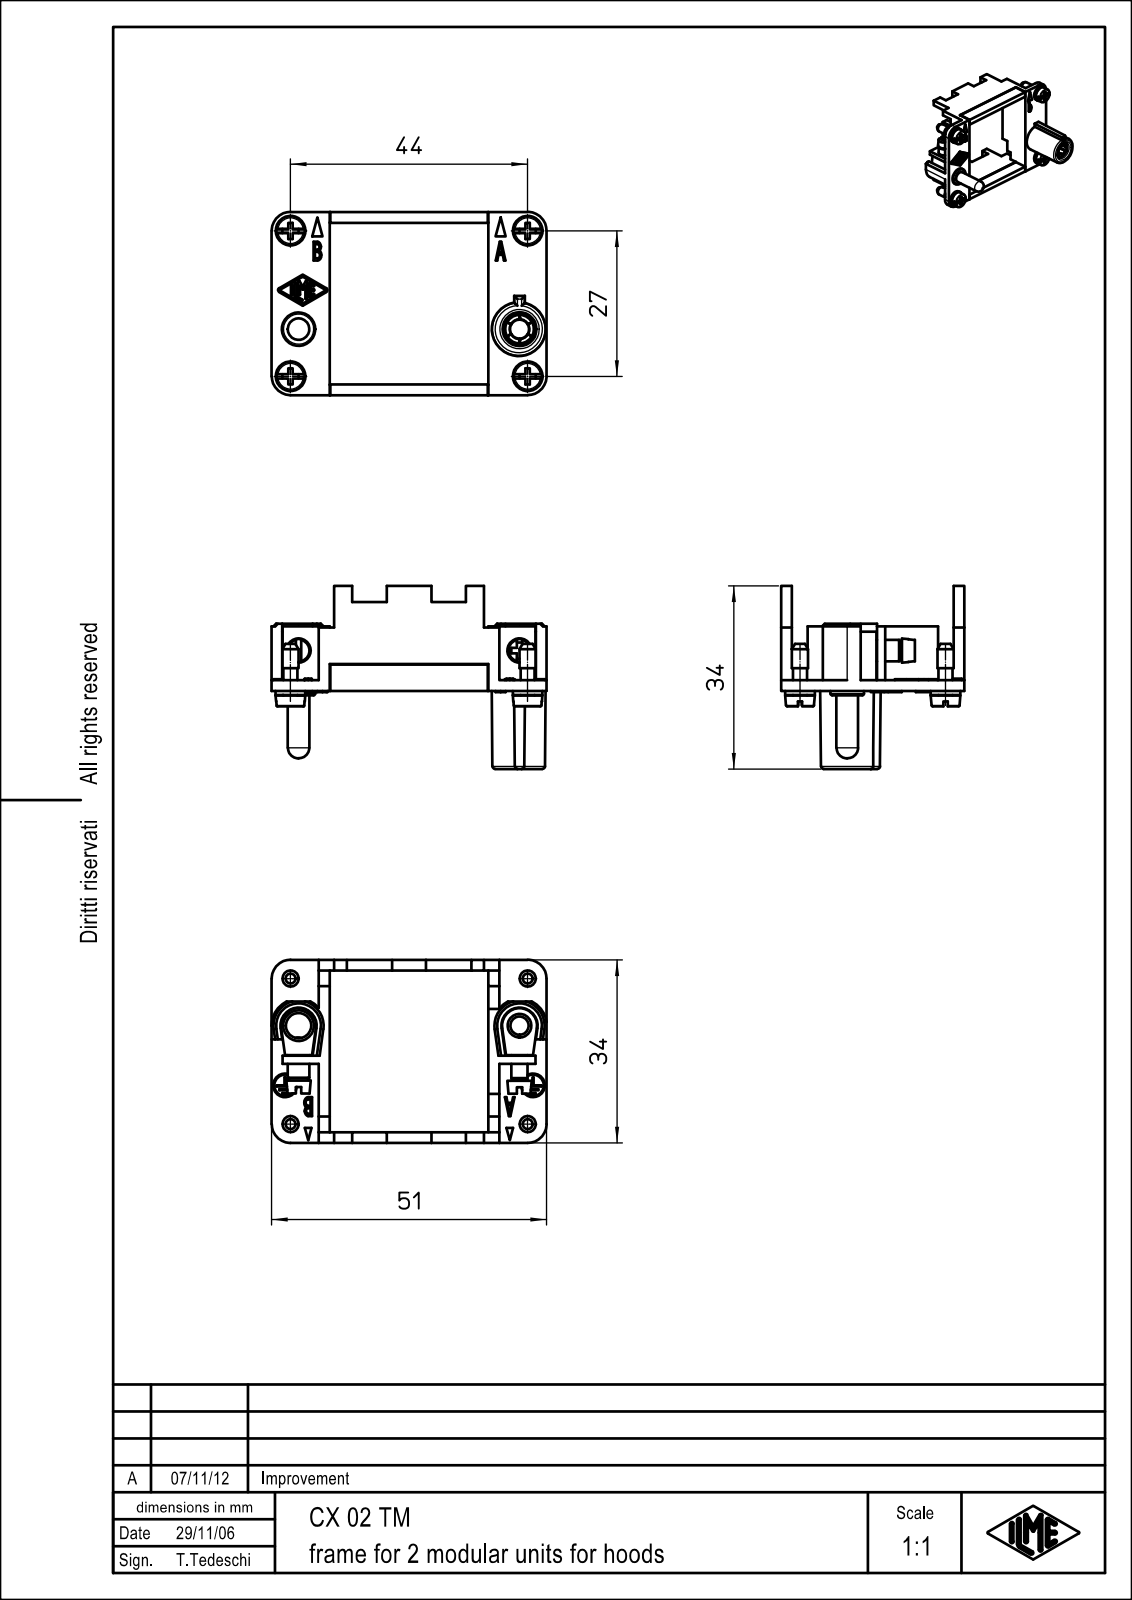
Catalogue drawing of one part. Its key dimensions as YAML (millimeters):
part_name: "CX_02_TM"
step_written_by: "Creo Elements/Direct Modeling 18.0B 02-Dec-2011 (C) Parametric Technology GmbH (AUTOMOTIVE_DESIGN)"
units: millimeters
bodies: {solids: 1, faces: 627, planar: 411, cylindrical: 104, other: 112}
overall_size: [51, 34, 34]
volume: 7683
surface_area: 9318
round_holes:
  - {diameter: 4, count: 2}
  - {diameter: 2.5, count: 1}
  - {diameter: 3.3, count: 1}
  - {diameter: 3.4, count: 1}
  - {diameter: 4.2, count: 1}
  - {diameter: 4.7, count: 1}
  - {diameter: 6.3, count: 1}
round_bosses_or_shafts:
  - {diameter: 3, count: 5}
  - {diameter: 5.5, count: 4}
  - {diameter: 2.6, count: 4}
  - {diameter: 4.4, count: 2}
  - {diameter: 4, count: 2}
  - {diameter: 6.2, count: 1}
  - {diameter: 6, count: 1}
  - {diameter: 3.5, count: 1}
partial_cylinders:
  - {radius: 0.17, count: 11}
  - {radius: 3.5, count: 4}
  - {radius: 0.5, count: 3}
  - {radius: 0.13, count: 2}
  - {radius: 0.41, count: 2}
  - {radius: 3.25, count: 2}
  - {radius: 3.35, count: 2}
  - {radius: 5, count: 2}
face_to_face_distances: [2, 32, 34, 30, 2.05, 31.45, 29.4, 2.85, 8.75, 40.2]
hole_center_spacings: [11.34, 41, 44.88, 44.89, 46.01]
